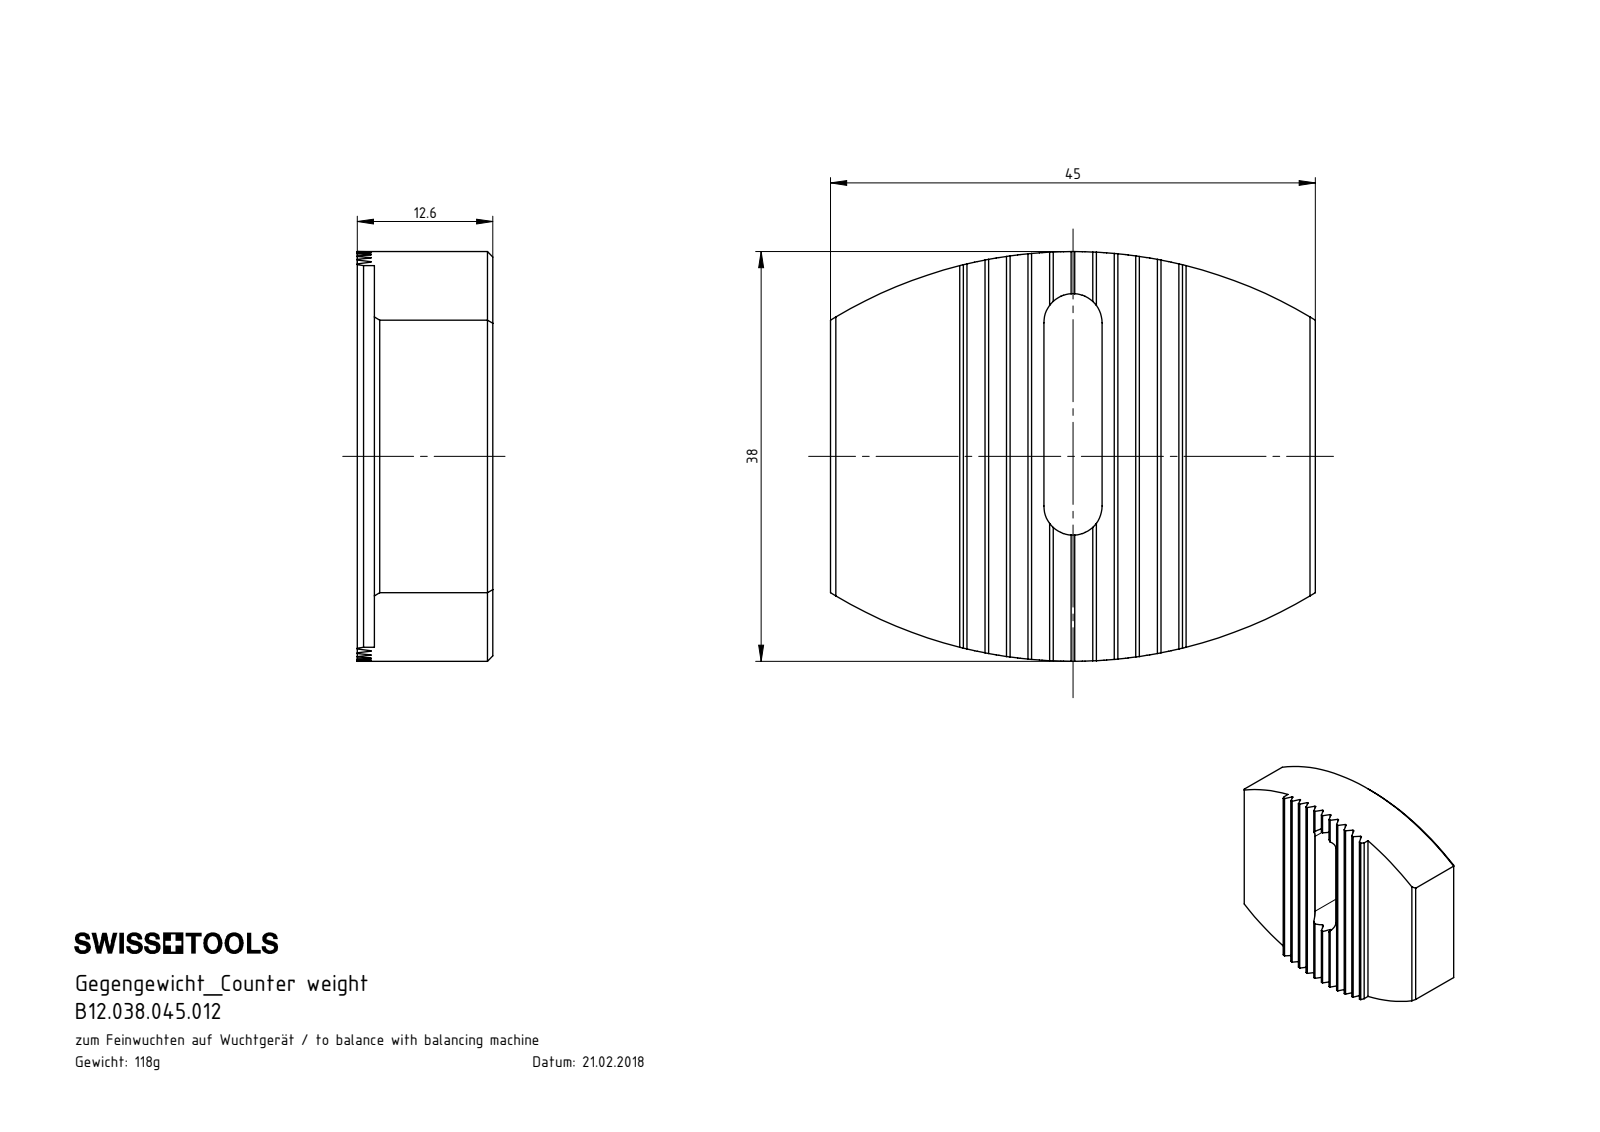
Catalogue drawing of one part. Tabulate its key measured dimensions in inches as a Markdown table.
| quantity | value |
| --- | --- |
| part name | B12.038.045.012 |
| STEP written by | SolidWorks 2017 (CONFIG_CONTROL_DESIGN) |
| units | inches |
| bodies | 1 solid, 90 faces (56 planar, 32 cylindrical, 2 other) |
| overall size | 1.772 × 1.496 × 0.495 |
| volume | 0.92 in³ |
| surface area | 8.792 in² |
| partial cylindrical surfaces (radius × count) | 0.006 × 10, 0.106 × 2, 0.226 × 2, 1.693 × 2 |
| main face-to-face distances | 0.433, 0.068, 0.205, 0.341, 0.136, 0.409, 0.273, 0.477, 1.772, 0.204 |
